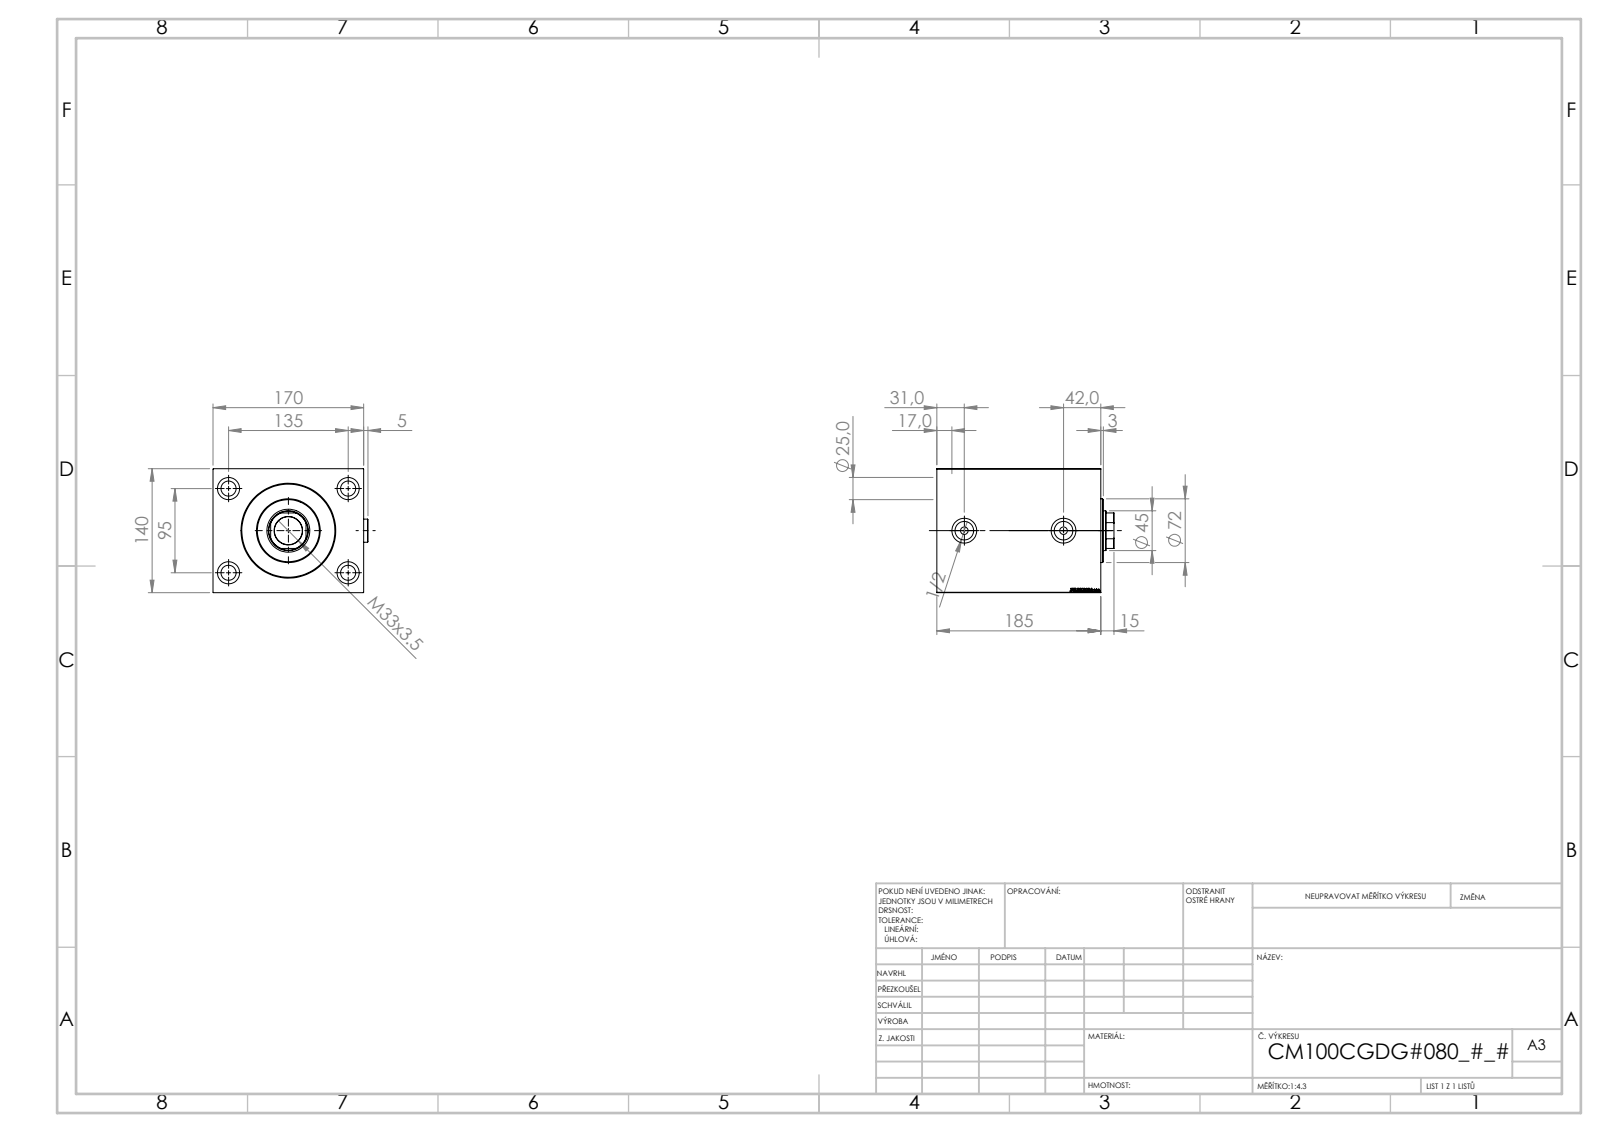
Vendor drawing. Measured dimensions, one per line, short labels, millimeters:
name: V450CM_VC_B; Zatka_OIL_PORT; V450CM_C_Body; V450CM_C_VCP
written by: SolidWorks 2019 (CONFIG_CONTROL_DESIGN)
unit: mm
bodies: 5 solids, 919 faces (443 planar, 78 cylindrical, 398 other)
size: 200 × 174.9 × 140
volume: 3 677 000 mm³; area: 338 904 mm²
holes: 4× ⌀17, 4× ⌀25, 2× ⌀8.5, 2× ⌀20.96, 2× ⌀28, 1× ⌀31.5, 1× ⌀45, 1× ⌀48.5, 1× ⌀100, 1× ⌀102, 1× ⌀105
bosses: 2× ⌀26, 1× ⌀72
rounds: 1× R22
face distances: 170, 140, 185, 159, 26, 90, 15, 144, 95, 80
hole spacings: 82.54, 95, 135, 165.08, 112
